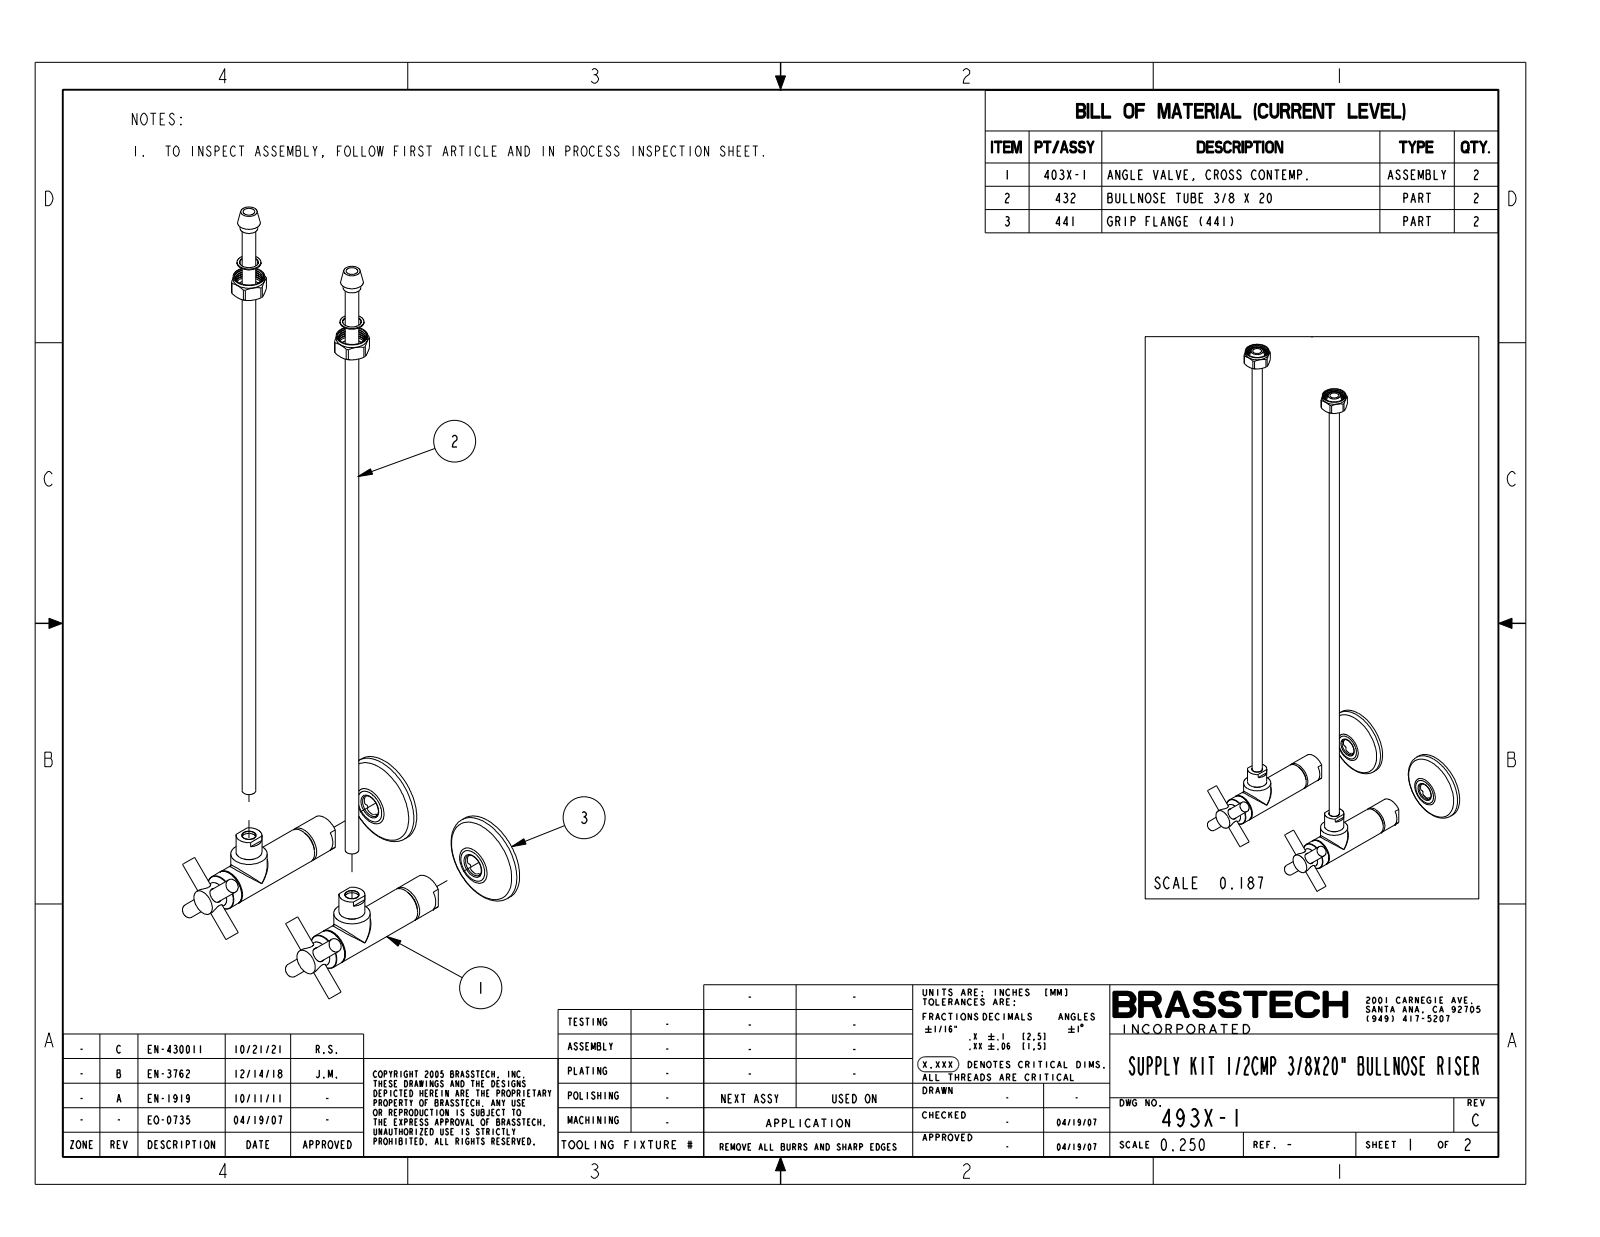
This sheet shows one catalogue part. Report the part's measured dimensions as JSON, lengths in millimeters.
{"part_name": "493X-1", "step_written_by": "CREO PARAMETRIC BY PTC INC, 2018500 (CONFIG_CONTROL_DESIGN)", "units": "millimeters", "bodies": {"solids": 16, "faces": 2574, "planar": 654, "cylindrical": 1218, "other": 702}, "overall_size": [546.3, 178.9, 165.1], "volume_mm3": 100300, "surface_area_mm2": 291700, "round_holes": [[9.8, 7], [3.8, 6], [4.8, 6], [10.3, 6], [3.7, 4], [8.1, 4], [3.7, 2], [7, 2], [7.6, 2], [8.3, 2], [9.5, 2], [9.6, 2]], "round_bosses_or_shafts": [[25.4, 4], [22.5, 2], [22, 2], [21, 2], [18, 2], [16.8, 2], [16.6, 2], [16.1, 2]], "partial_cylinders_radius": [[0.8, 18], [1.5, 9], [0.1, 4], [3.4, 2], [5.1, 2], [12.4, 2], [1.8, 1], [11, 1]], "face_to_face_distances": [22.2, 102.7, 44.5, 88, 88, 20.7, 82, 63.7, 43, 39], "hole_center_spacings": [71.8, 101.6, 1.1, 101.6]}
